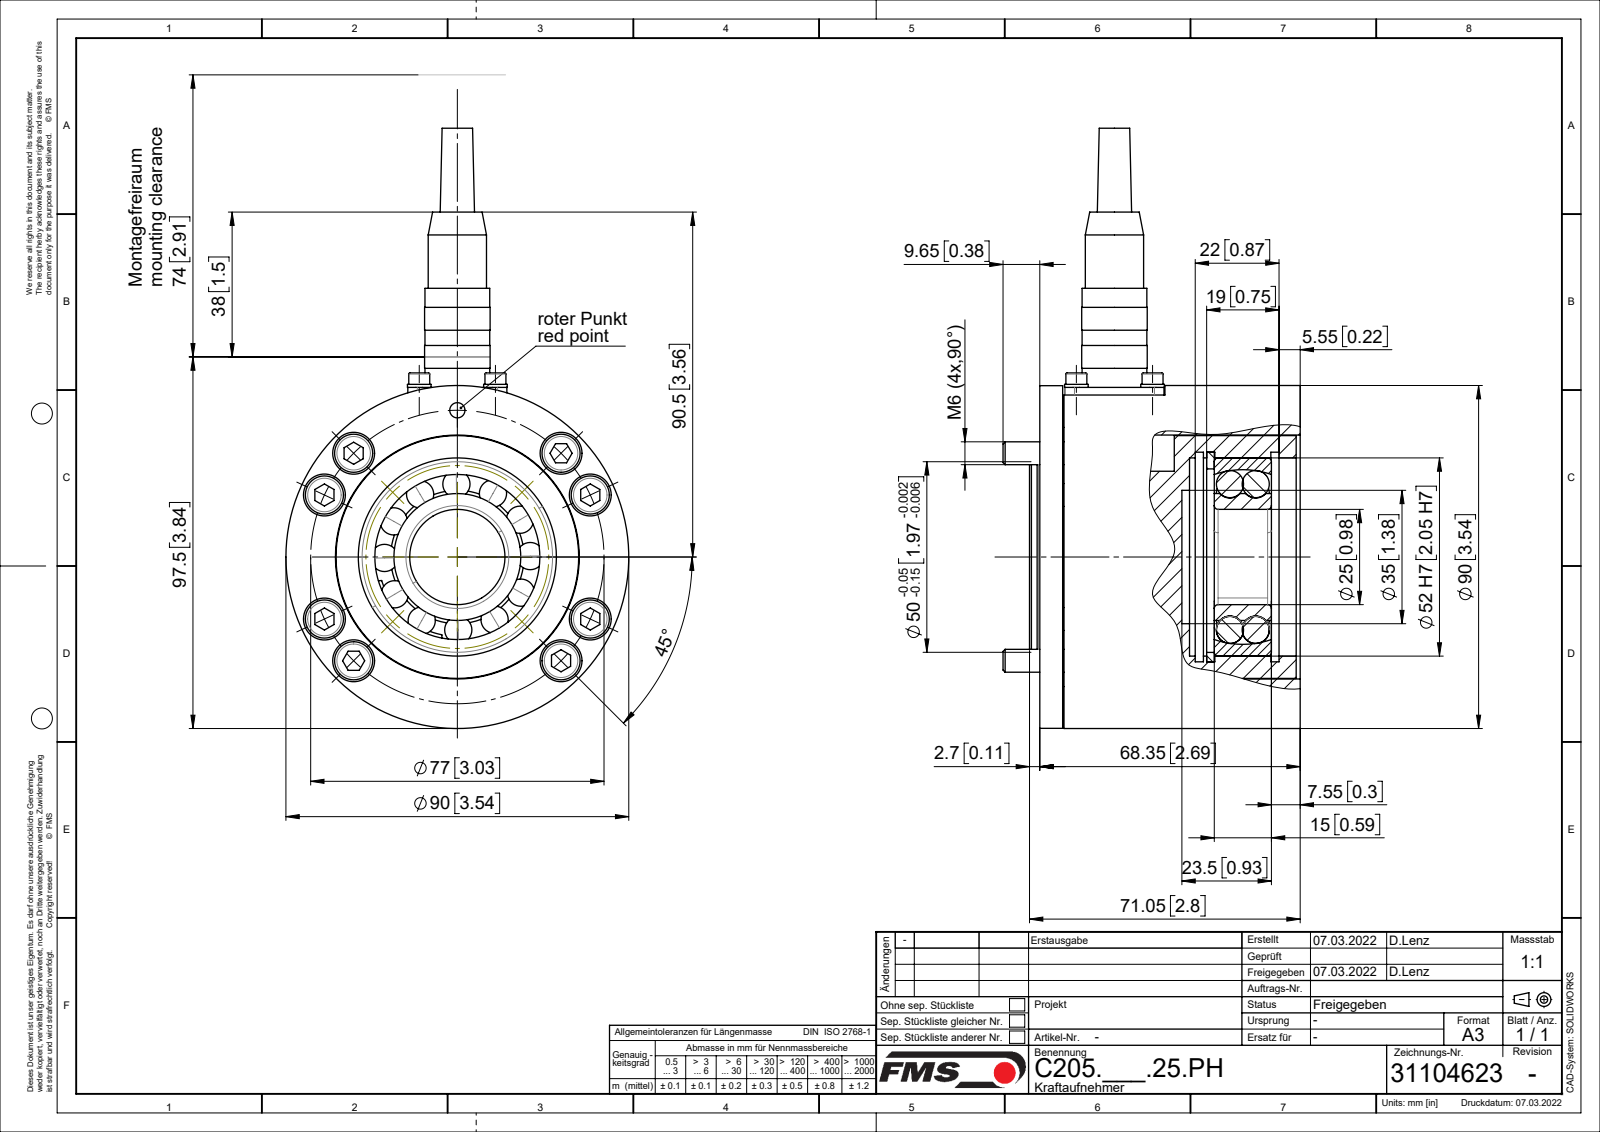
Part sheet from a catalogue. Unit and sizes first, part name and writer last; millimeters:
Units: millimetres
Overall size (bounding box): 157.5 × 90 × 78
Round holes (diameter × count): ⌀6.5 ×8, ⌀11 ×8, ⌀2.5 ×6, ⌀3.1 ×4, ⌀3.2 ×4, ⌀5 ×4, ⌀7 ×4, ⌀4 ×2, ⌀10.2 ×1, ⌀12 ×1, ⌀15 ×1, ⌀18 ×1
Round bosses / shafts (diameter × count): ⌀10 ×8, ⌀6 ×8, ⌀1.5 ×5, ⌀6.2 ×4, ⌀5.5 ×4, ⌀3 ×4, ⌀90 ×1, ⌀89.9 ×1
Partial cylindrical surfaces — rounded edges, fillets, slot ends (radius × count): R0.1 ×4, R2.5 ×4, R4.24 ×2, R5 ×2, R20.8 ×1, R24.1 ×1
Main face-to-face distances: 6, 3.3, 2.7, 2, 6.5, 32, 33.05, 38, 30, 29.3
Hole centre spacings: 20, 38.5, 13.37, 14.14, 38.49, 44.16, 54.44, 63.07
Volume: 307 329 mm³ · Surface area: 123 450 mm²
Bodies: 48 solids, 630 faces (206 planar, 260 cylindrical, 164 other)
Part name (STEP PRODUCT): 31104488_01; PKL_1205_01; Si-Ring DIN472_D52x2; Zyl-Schr DIN912_M3x6 (+8 more)
STEP written by: SolidWorks 2018 (CONFIG_CONTROL_DESIGN)
